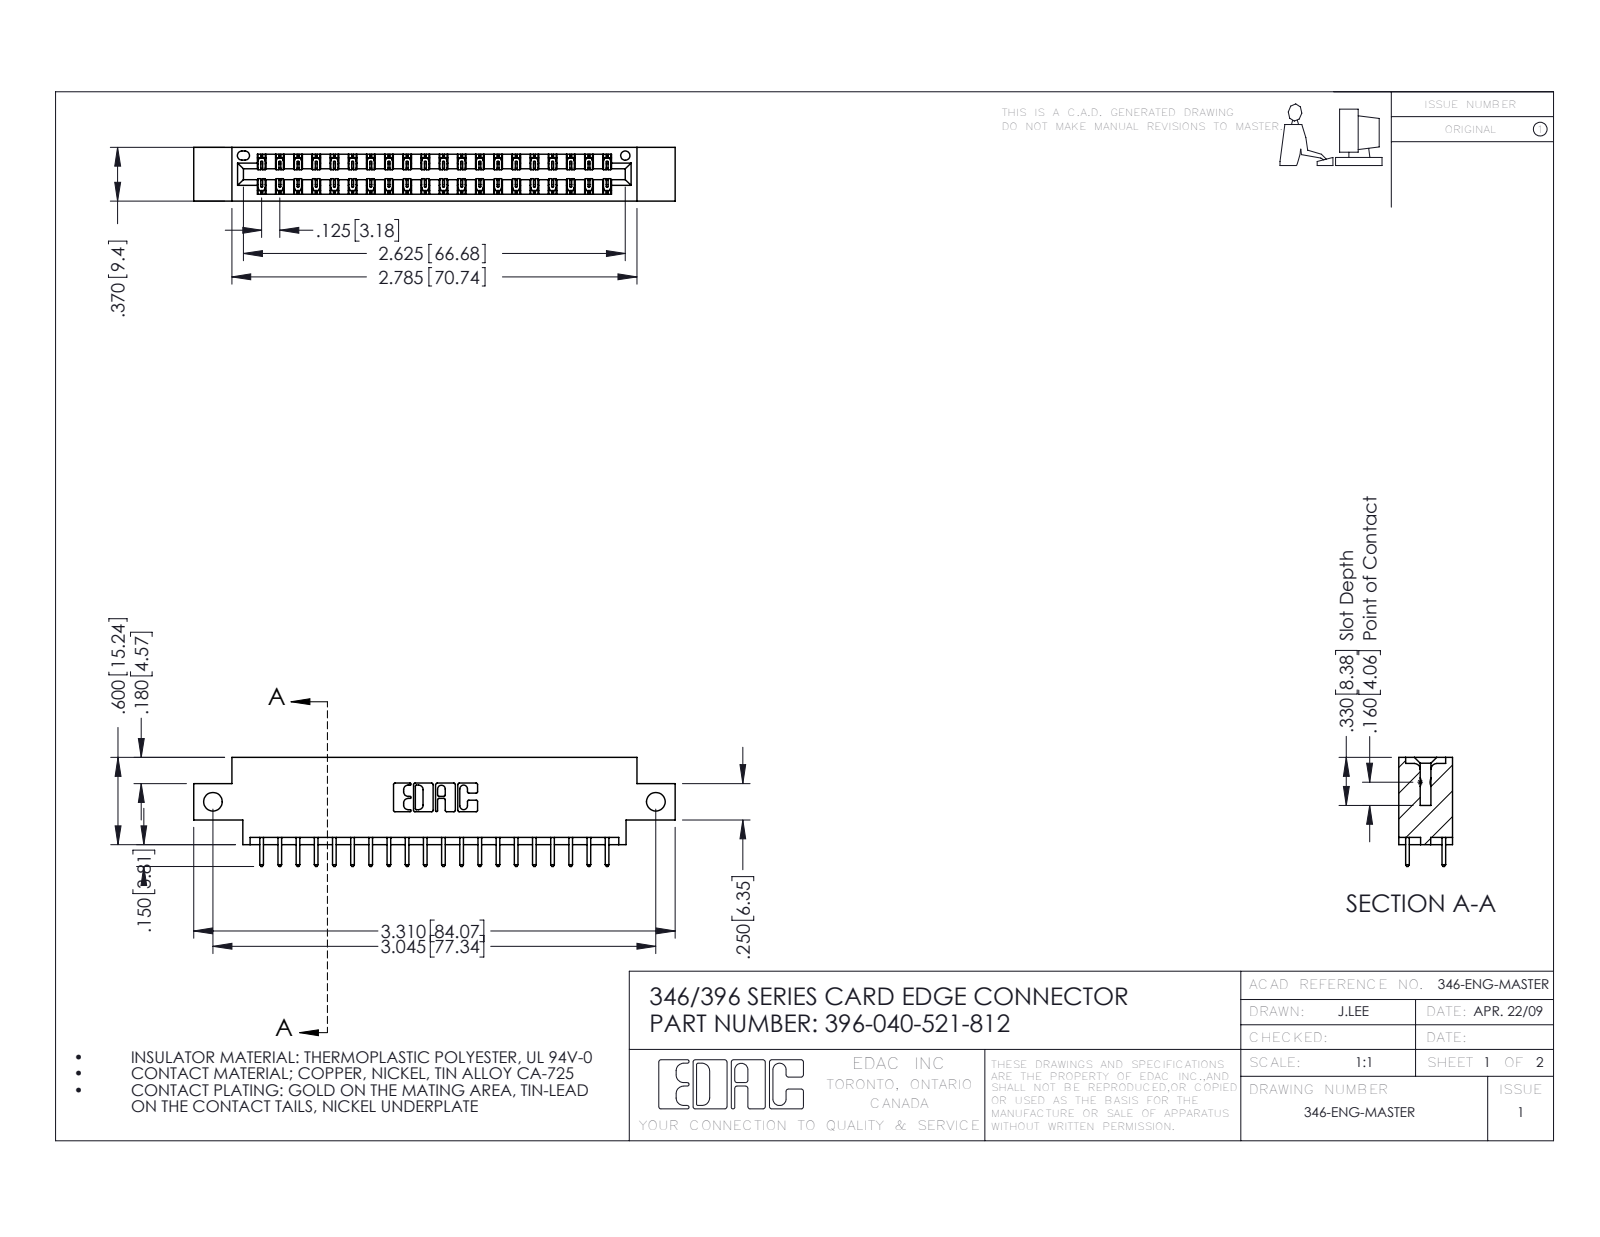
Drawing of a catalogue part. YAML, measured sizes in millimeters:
part_name: "396-040-521-812; 346 Part_0.170 Offset - Side Mount; 345-292-001_345-293-121"
step_written_by: "SolidWorks 2016 (CONFIG_CONTROL_DESIGN)"
units: millimeters
bodies: {solids: 41, faces: 2206, planar: 1480, cylindrical: 726, other: 0}
overall_size: [84.1, 19.1, 9.4]
volume: 7770
surface_area: 10260
round_holes:
  - {diameter: 3.3, count: 2}
  - {diameter: 1.6, count: 1}
partial_cylinders:
  - {radius: 0.2, count: 60}
  - {radius: 0.3, count: 40}
  - {radius: 0.3, count: 22}
  - {radius: 0.2, count: 6}
  - {radius: 0.8, count: 6}
  - {radius: 0.7, count: 3}
  - {radius: 0.4, count: 2}
  - {radius: 0.6, count: 2}
face_to_face_distances: [1.2, 8.2, 6.4, 9.4, 1.8, 7.6, 0.6, 7, 3.8, 5.6]
hole_center_spacings: [77.3]
